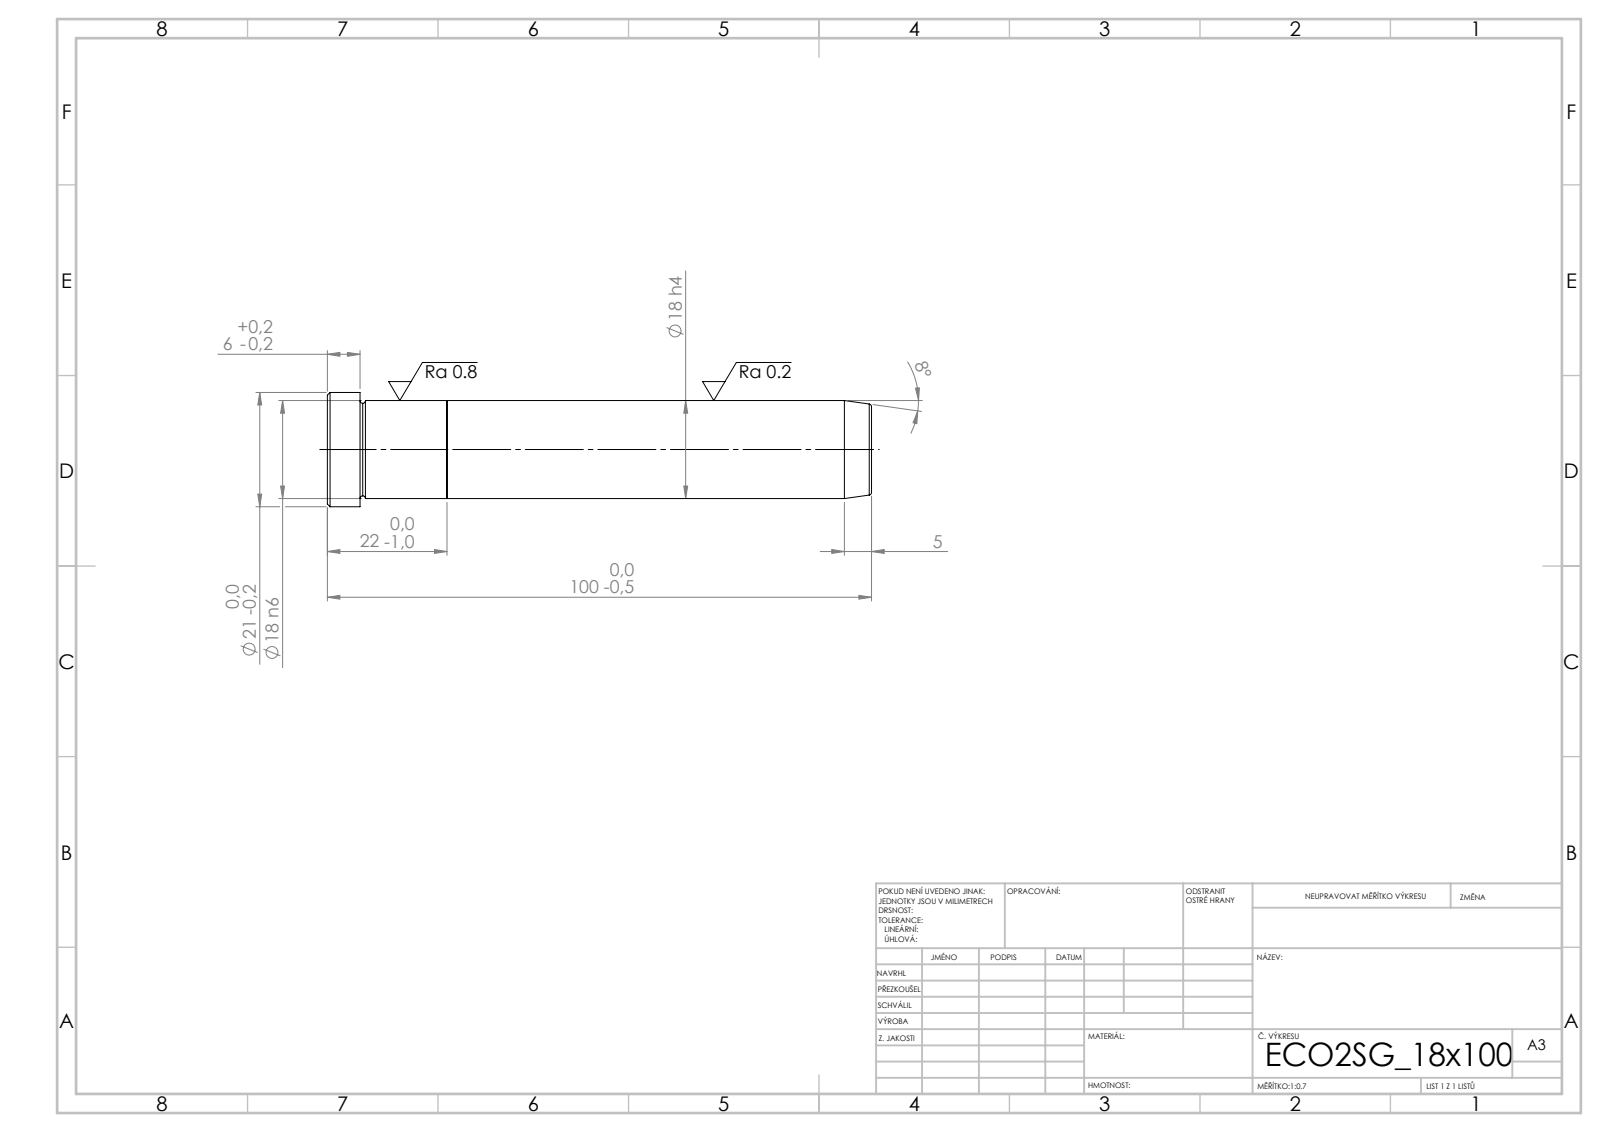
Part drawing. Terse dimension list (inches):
written by: SolidWorks 2019 (CONFIG_CONTROL_DESIGN)
unit: in
bodies: 2 solids, 21 faces (5 planar, 6 cylindrical, 10 other)
size: 3.937 × 0.827 × 0.827
volume: 1.579 in³; area: 10.65 in²
bosses: 1× ⌀0.827, 1× ⌀0.709
face distances: 0.866, 3.071, 3.937, 3.701, 0.63, 0.236
